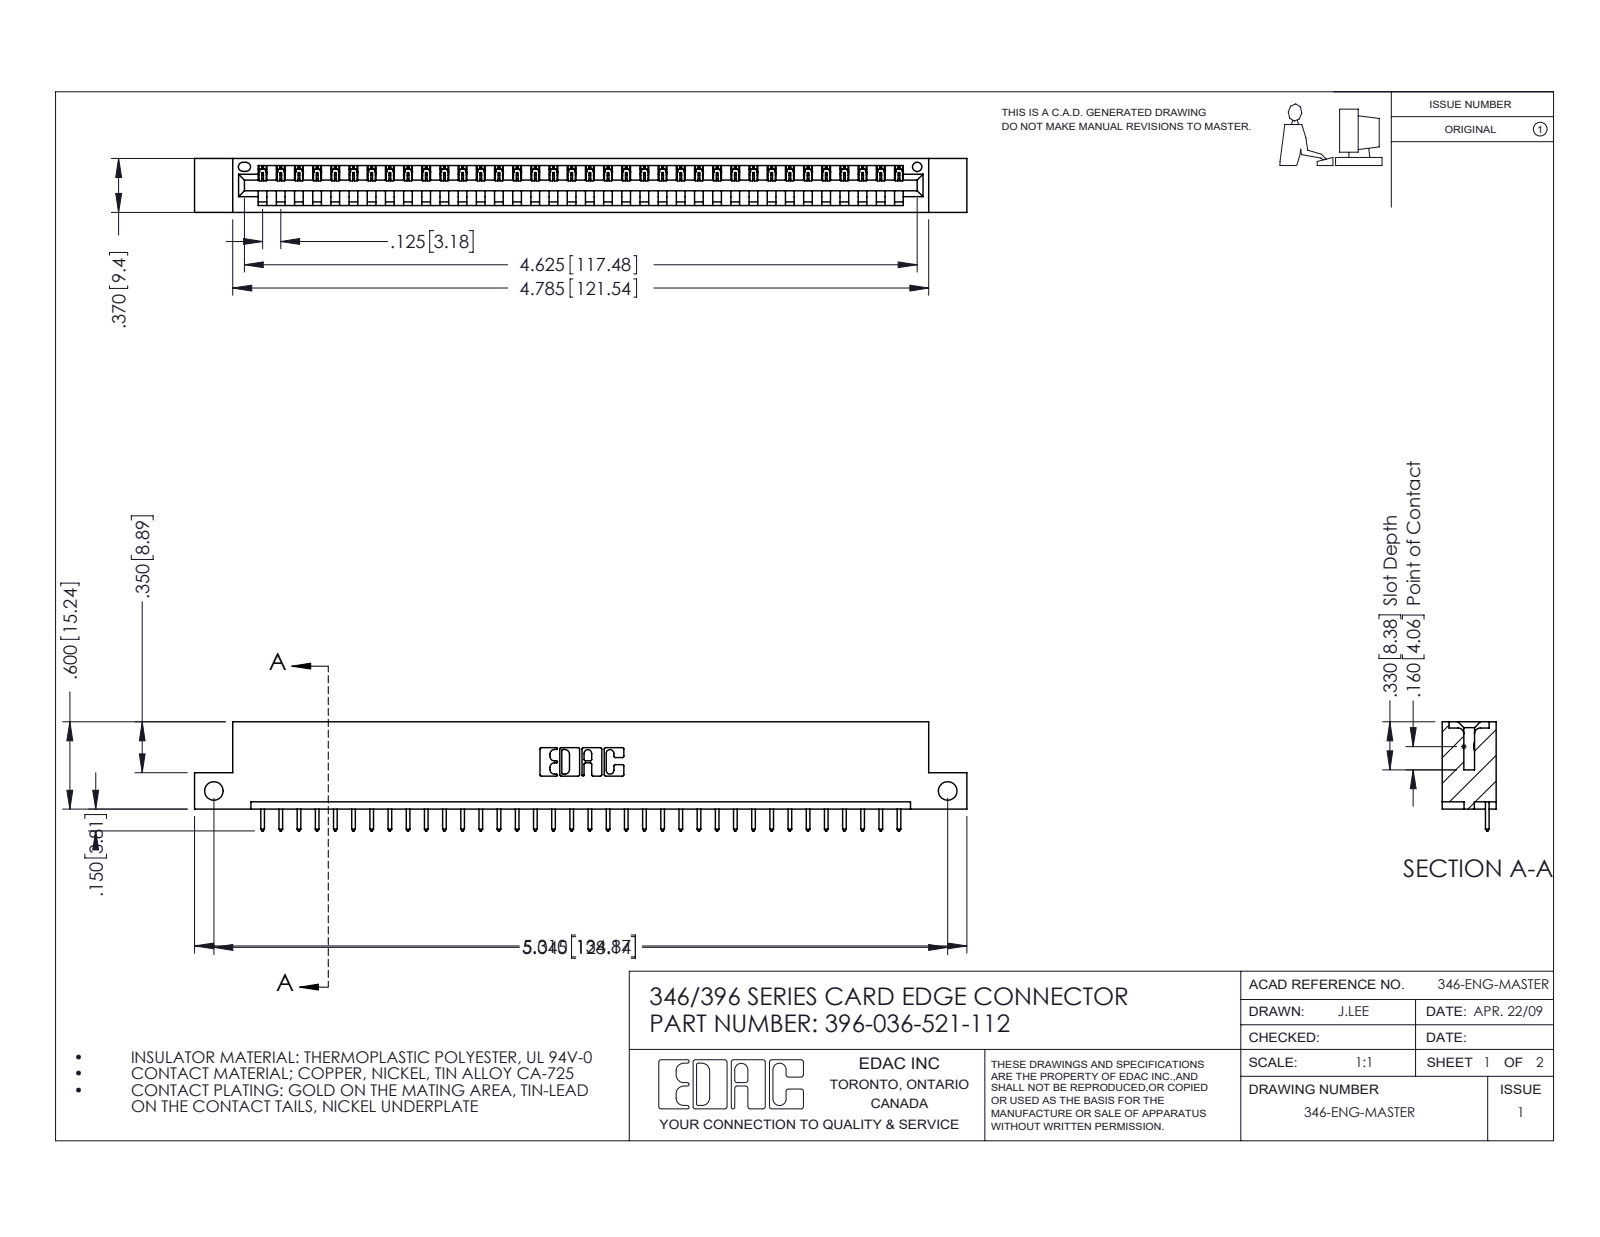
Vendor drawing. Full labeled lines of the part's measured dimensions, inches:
Part name (STEP PRODUCT): 345-292-001_345-293-121; 396-036-521-112; 346 Part_Flush Mounting Lugs - Side Mount
STEP written by: SolidWorks 2016 (CONFIG_CONTROL_DESIGN)
Units: inches
Bodies: 37 solids, 2210 faces (1516 planar, 694 cylindrical, 0 other)
Overall size (bounding box): 5.31 × 0.75 × 0.37
Volume: 0.774 in³ · Surface area: 23.61 in²
Round holes (diameter × count): ⌀0.128 ×2, ⌀0.064 ×1
Partial cylindrical surfaces — rounded edges, fillets, slot ends (radius × count): R0.006 ×72, R0.01 ×72, R0.01 ×22, R0.007 ×6, R0.031 ×6, R0.026 ×3, R0.031 ×2, R0.04 ×2
Main face-to-face distances: 0.048, 0.322, 0.37, 0.25, 0.072, 0.298, 0.025, 0.148, 0.222, 0.1
Hole centre spacings: 5.045
